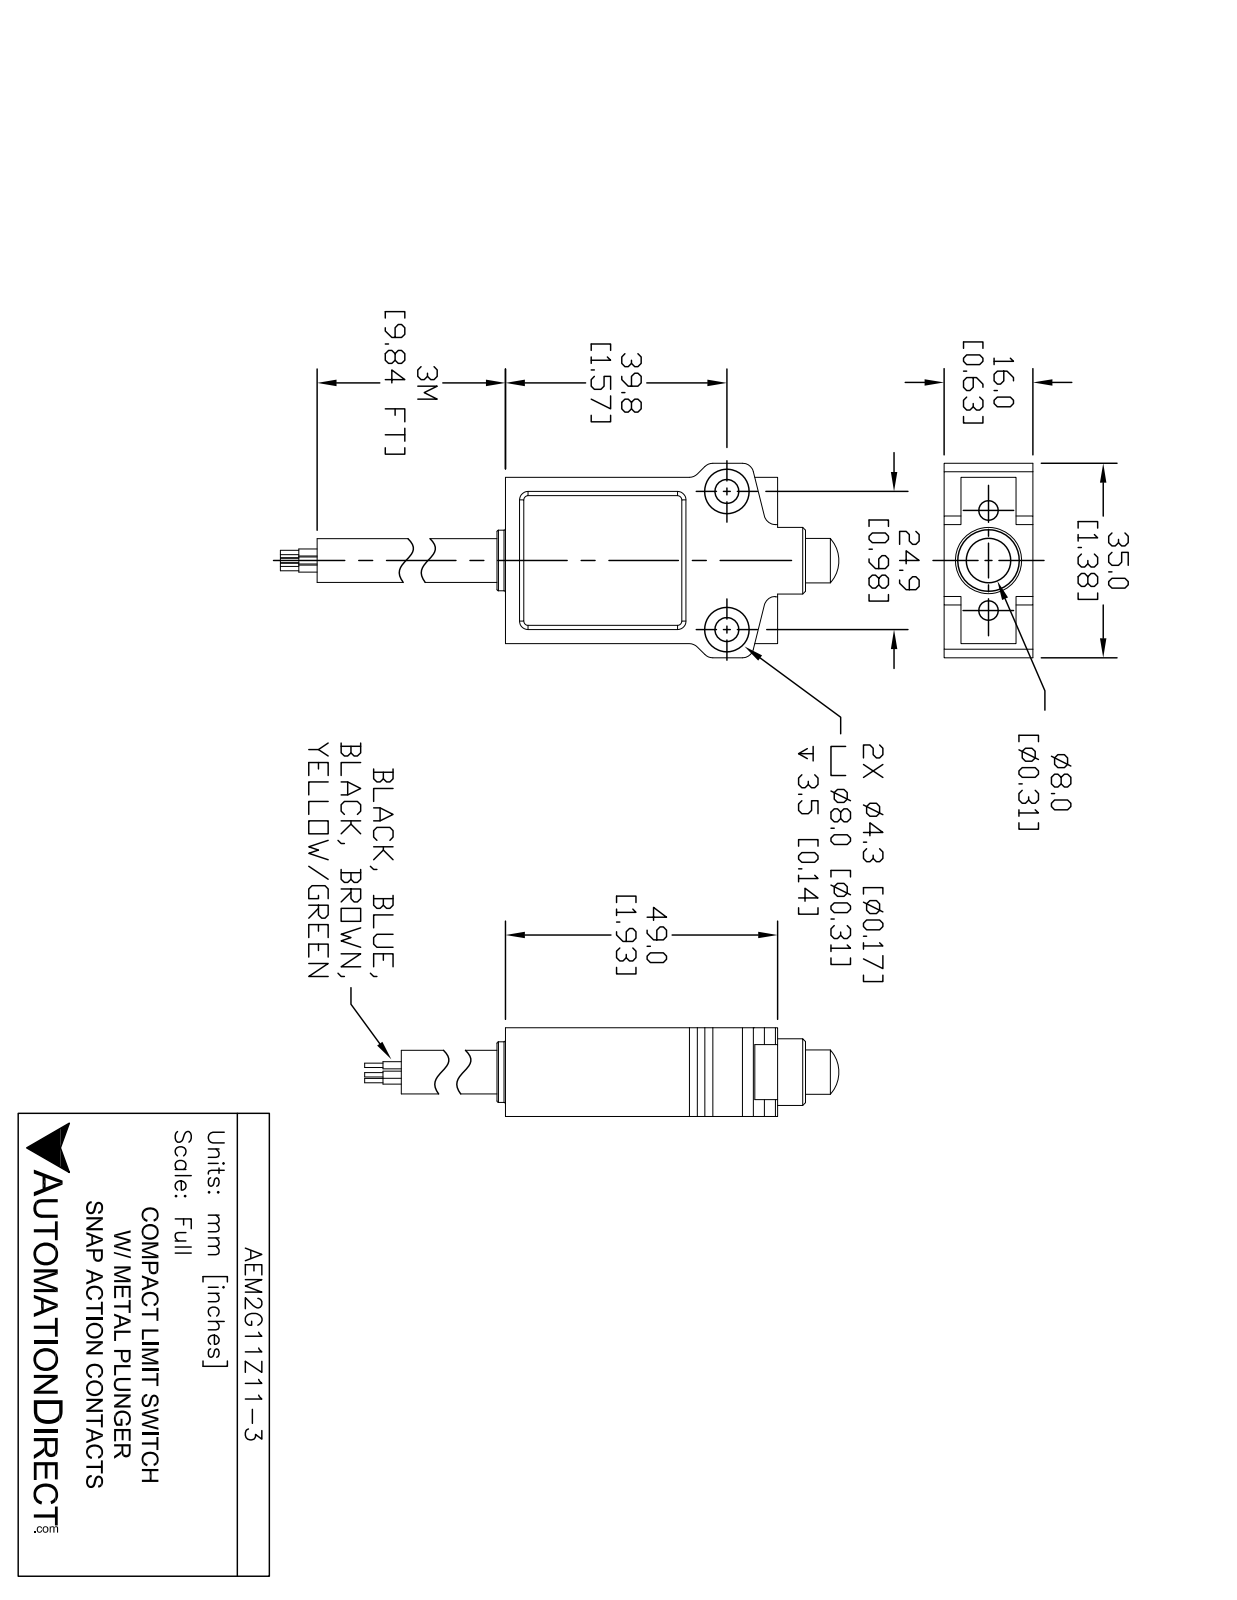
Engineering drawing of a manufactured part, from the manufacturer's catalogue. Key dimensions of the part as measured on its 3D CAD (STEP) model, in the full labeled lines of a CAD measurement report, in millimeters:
Part name (STEP PRODUCT): AEM2G11Z11-3_Default
STEP written by: SolidWorks 2021 (CONFIG_CONTROL_DESIGN)
Units: millimetres
Bodies: 1 solid, 99 faces (43 planar, 40 cylindrical, 16 other)
Overall size (bounding box): 75.2 × 35.1 × 16
Volume: 22 730 mm³ · Surface area: 7 032 mm²
Round holes (diameter × count): ⌀3.5 ×2, ⌀4.5 ×2, ⌀8.7 ×2
Round bosses / shafts (diameter × count): ⌀1.3 ×5, ⌀0.8 ×5, ⌀11.9 ×1, ⌀10.9 ×1, ⌀7.9 ×1
Partial cylindrical surfaces — rounded edges, fillets, slot ends (radius × count): R0.8 ×8, R2 ×8
Main face-to-face distances: 0.8, 15.2, 14.5, 16, 30, 49, 4.7, 11.3, 4, 10.5
Hole centre spacings: 17.8, 24.9
